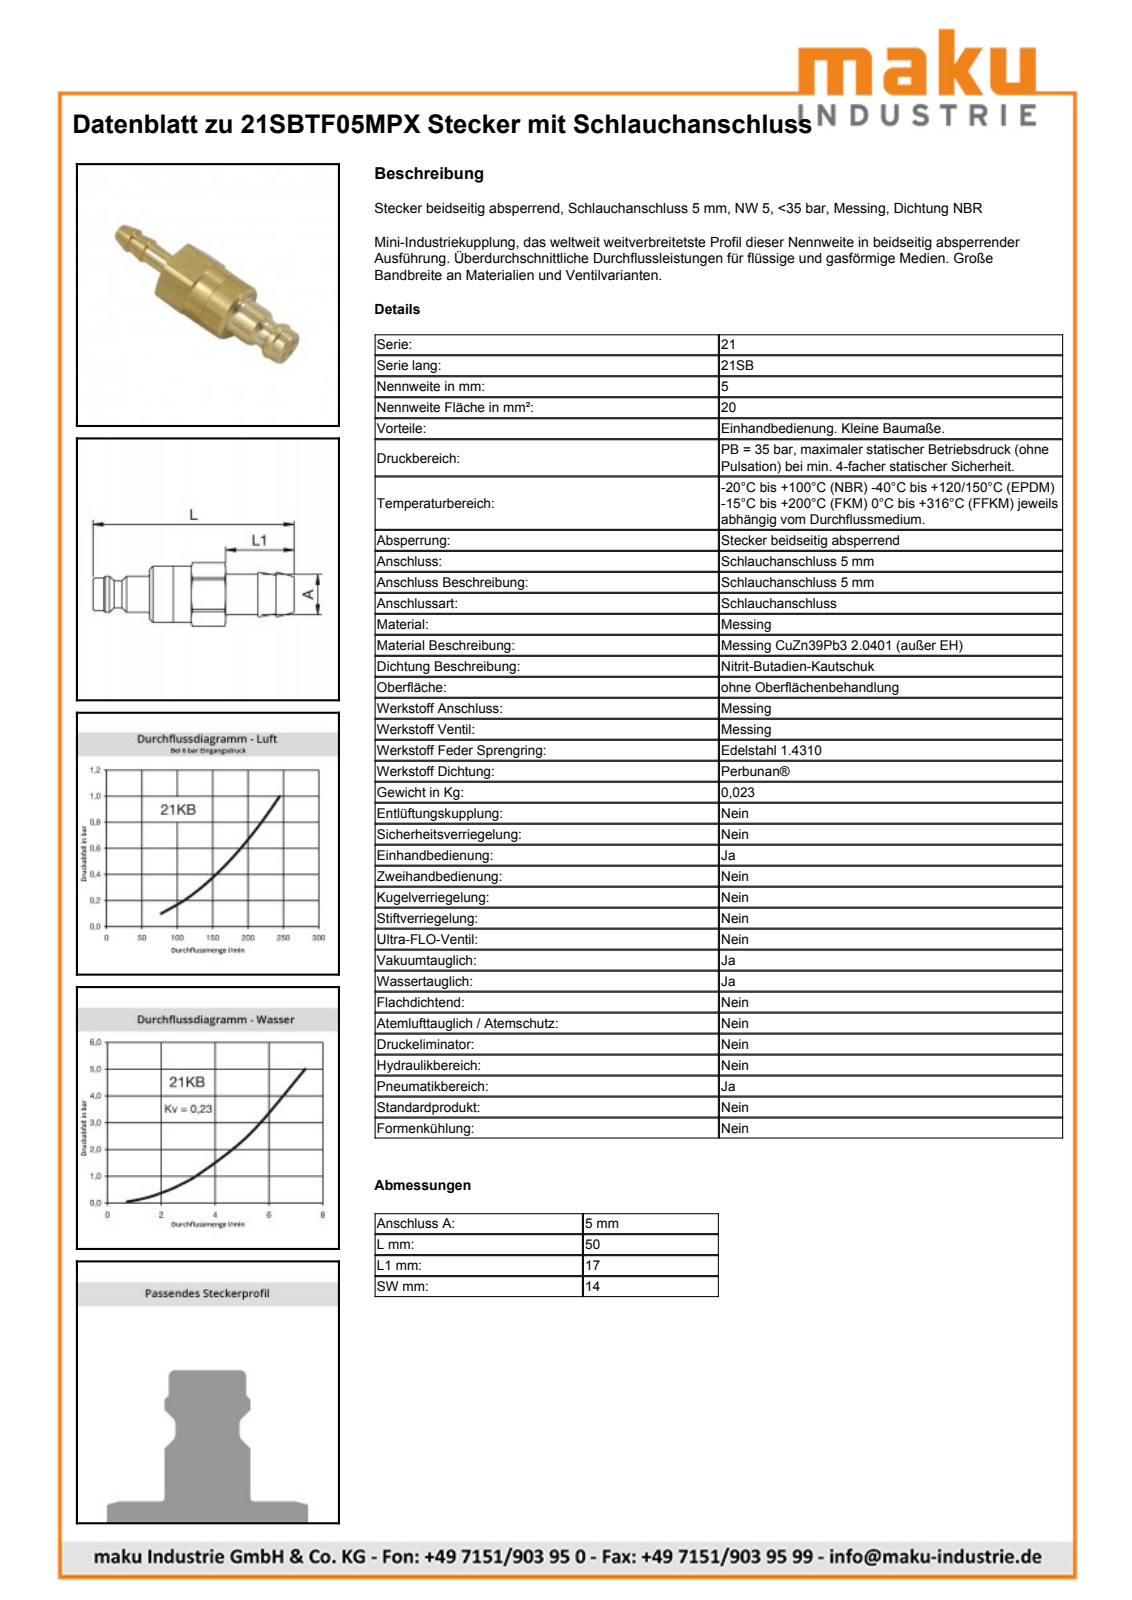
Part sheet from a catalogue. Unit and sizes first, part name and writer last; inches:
Units: inches
Overall size (bounding box): 1.969 × 0.614 × 0.598
Round holes (diameter × count): ⌀0.118 ×1, ⌀0.165 ×1, ⌀0.217 ×1, ⌀0.283 ×1, ⌀0.374 ×1, ⌀0.411 ×1, ⌀0.472 ×1
Round bosses / shafts (diameter × count): ⌀0.551 ×1, ⌀0.472 ×1, ⌀0.433 ×1, ⌀0.354 ×1, ⌀0.319 ×1, ⌀0.262 ×1, ⌀0.199 ×1
Partial cylindrical surfaces — rounded edges, fillets, slot ends (radius × count): R0.311 ×1
Main face-to-face distances: 0.551, 0.079, 0.433, 0.512, 0.232, 0.665, 0.744, 0.354, 0.39, 0.157
Volume: 0.145 in³ · Surface area: 5.149 in²
Bodies: 2 solids, 75 faces (16 planar, 22 cylindrical, 37 other)
Part name (STEP PRODUCT): D102680; GST21F05MXX; 21SBTF05MPX
STEP written by: Autodesk Inventor 2016 (AUTOMOTIVE_DESIGN)
